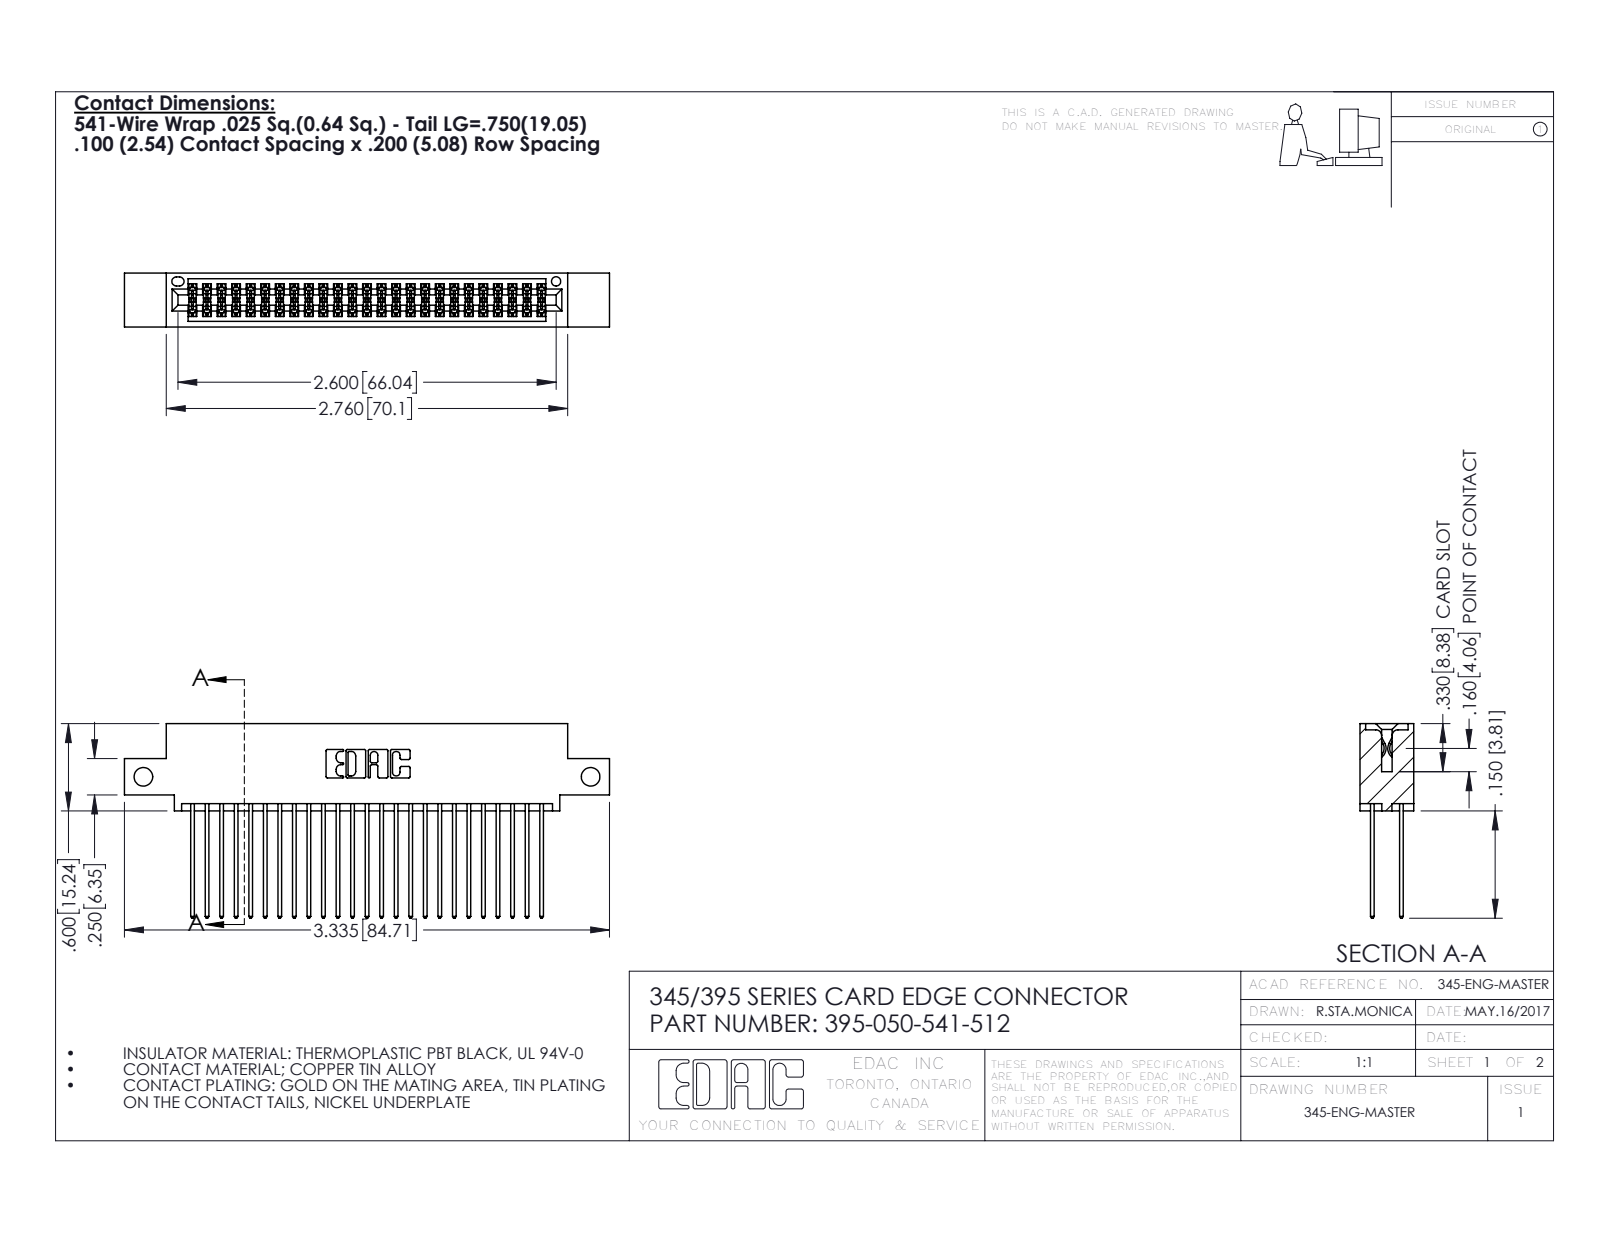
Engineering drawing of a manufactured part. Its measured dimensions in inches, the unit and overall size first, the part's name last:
Units: inches
Overall size (bounding box): 3.335 × 1.337 × 0.37
Round holes (diameter × count): ⌀0.128 ×2, ⌀0.064 ×1
Partial cylindrical surfaces — rounded edges, fillets, slot ends (radius × count): R0.006 ×75, R0.01 ×50, R0.01 ×22, R0.007 ×6, R0.031 ×6, R0.026 ×3, R0.014 ×2, R0.019 ×2
Main face-to-face distances: 0.072, 0.298, 0.2, 0.098, 0.272, 0.025, 0.225, 0.37, 0.175, 0.149
Hole centre spacings: 3.075
Volume: 0.5 in³ · Surface area: 20.29 in²
Bodies: 51 solids, 2630 faces (1734 planar, 896 cylindrical, 0 other)
Part name (STEP PRODUCT): 395-050-541-512; 345 Part_0.110 Offset - Side Mount; 345-292-001_345-293-141
STEP written by: SolidWorks 2016 (CONFIG_CONTROL_DESIGN)
